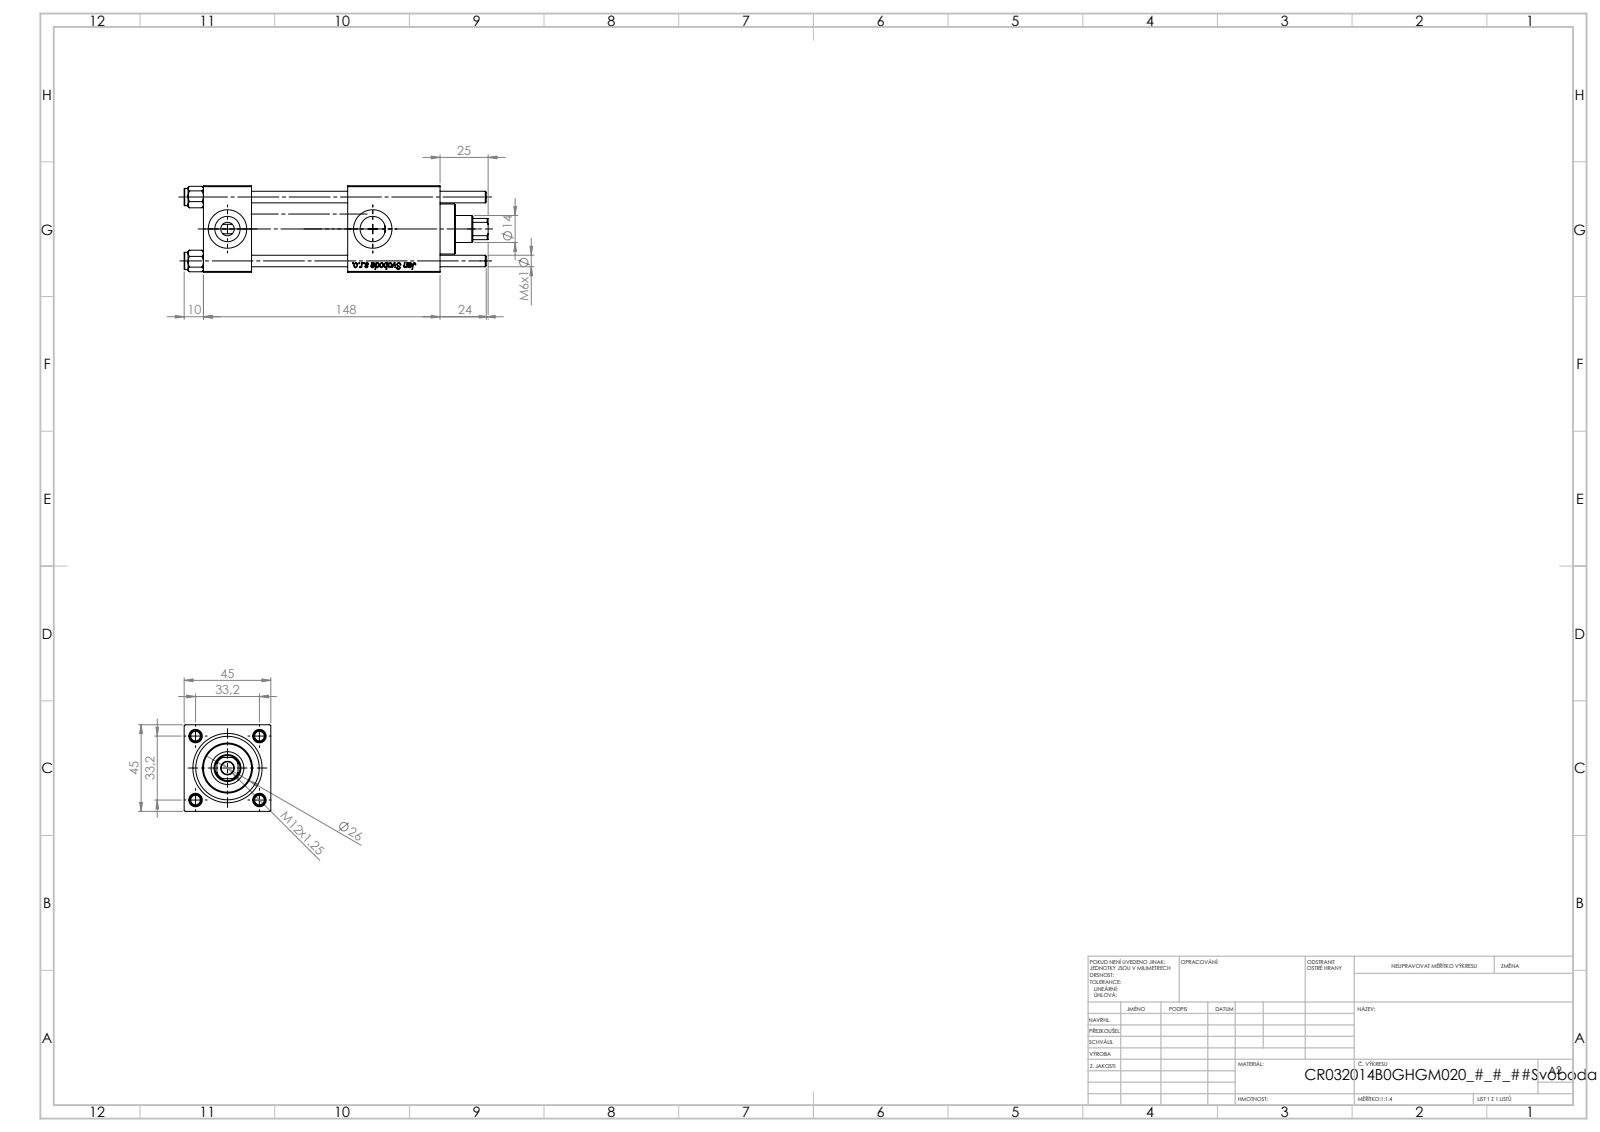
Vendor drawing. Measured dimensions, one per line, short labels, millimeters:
name: V215CR_B-1; V215_VC_A; NUT_M5_B; V215CR_B_TYCINKA (+1 more)
written by: SolidWorks 2019 (CONFIG_CONTROL_DESIGN)
unit: mm
bodies: 11 solids, 1157 faces (431 planar, 78 cylindrical, 648 other)
size: 158 × 45 × 45
volume: 198 372 mm³; area: 72 571 mm²
holes: 4× ⌀6, 2× ⌀7, 2× ⌀13.16, 2× ⌀20, 1× ⌀6.5, 1× ⌀14, 1× ⌀17, 1× ⌀24, 1× ⌀32, 1× ⌀33
bosses: 4× ⌀9, 1× ⌀38, 1× ⌀26
rounds: 1× R6.5
face distances: 45, 25, 123, 98, 50, 75, 48, 94.3, 69.3, 19.3
hole spacings: 23.48, 33.2, 46.95, 75.5
